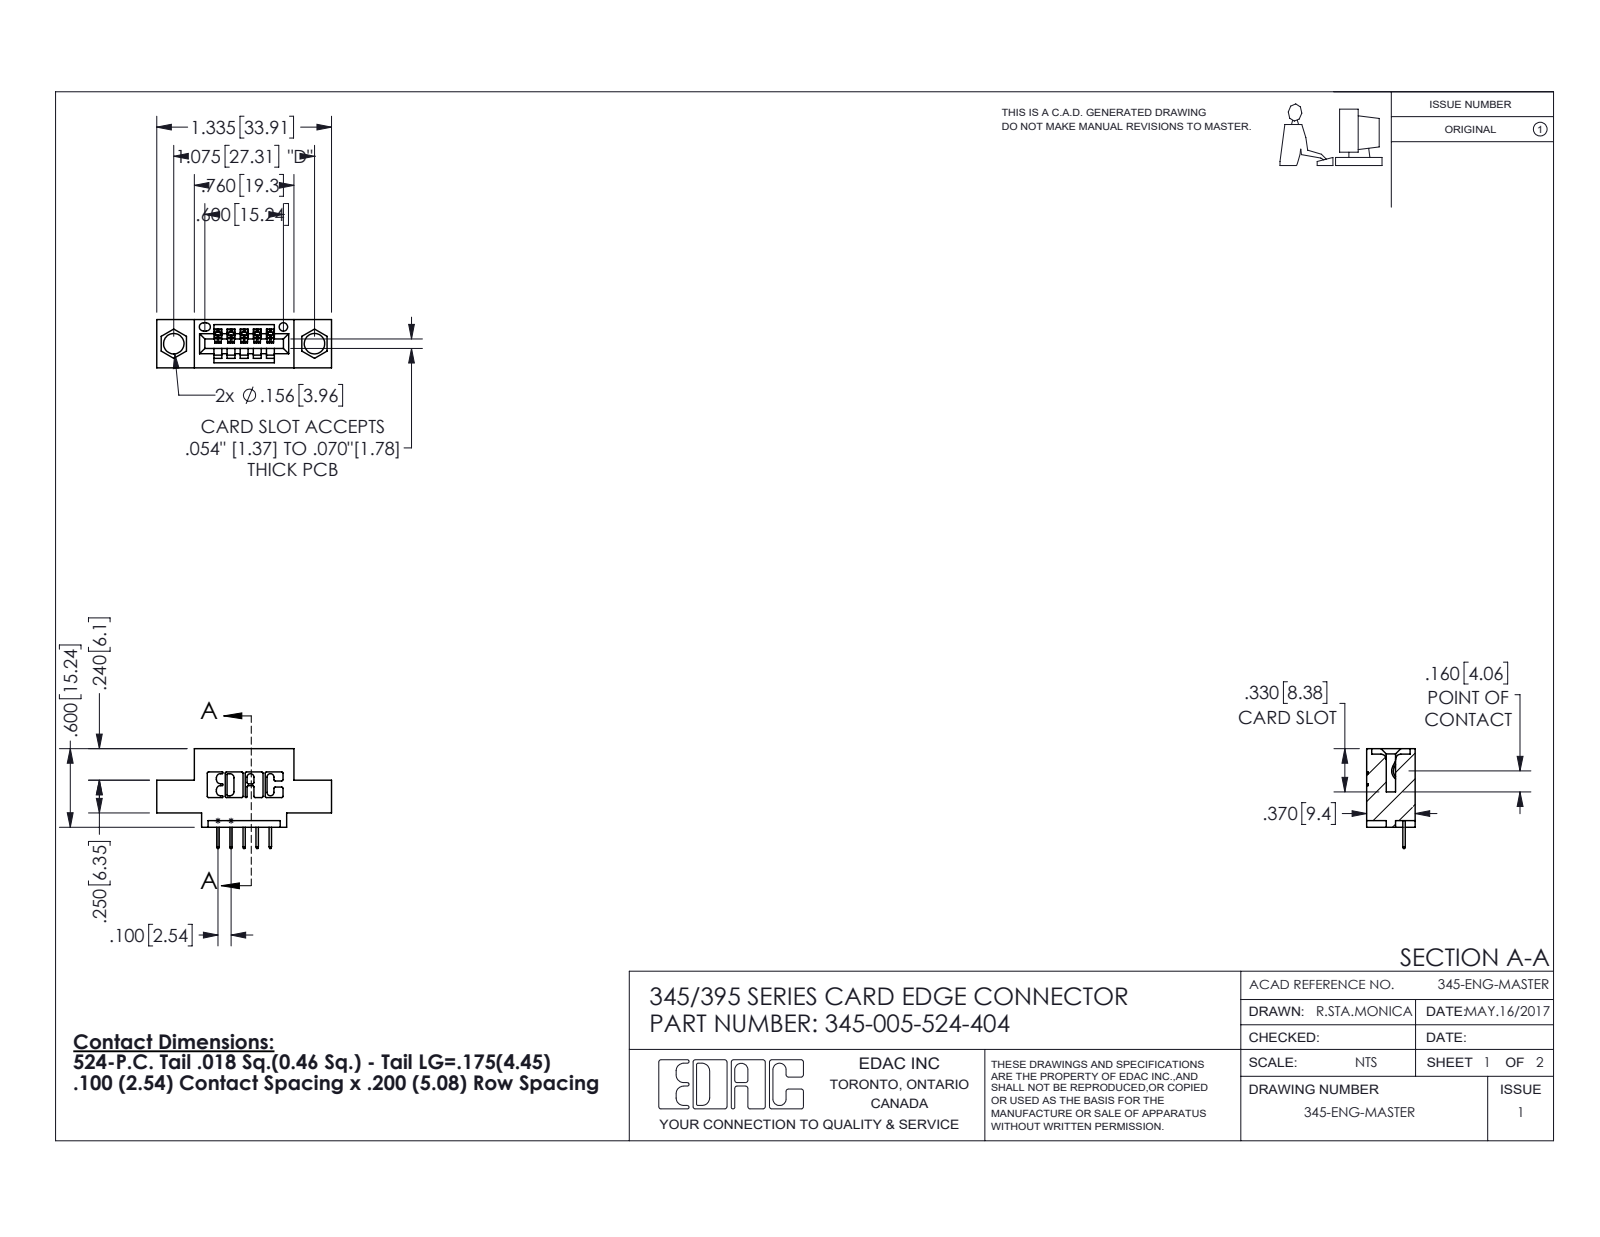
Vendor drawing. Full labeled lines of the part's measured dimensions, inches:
Part name (STEP PRODUCT): 345-292-001_345-293-124; 345 Part_0.110 Offset - 0.156 Dia-TH; 345-005-524-404
STEP written by: SolidWorks 2016 (CONFIG_CONTROL_DESIGN)
Units: inches
Bodies: 6 solids, 440 faces (314 planar, 126 cylindrical, 0 other)
Overall size (bounding box): 1.335 × 0.762 × 0.37
Volume: 0.167 in³ · Surface area: 4.59 in²
Round holes (diameter × count): ⌀0.156 ×2, ⌀0.064 ×1
Partial cylindrical surfaces — rounded edges, fillets, slot ends (radius × count): R0.01 ×22, R0.006 ×10, R0.007 ×6, R0.031 ×6, R0.026 ×3, R0.031 ×2, R0.04 ×2, R0.014 ×1
Main face-to-face distances: 0.37, 0.2, 0.1, 0.072, 0.298, 0.25, 0.025, 0.06, 0.16, 0.55
Hole centre spacings: 0.27, 0.847, 1.075
